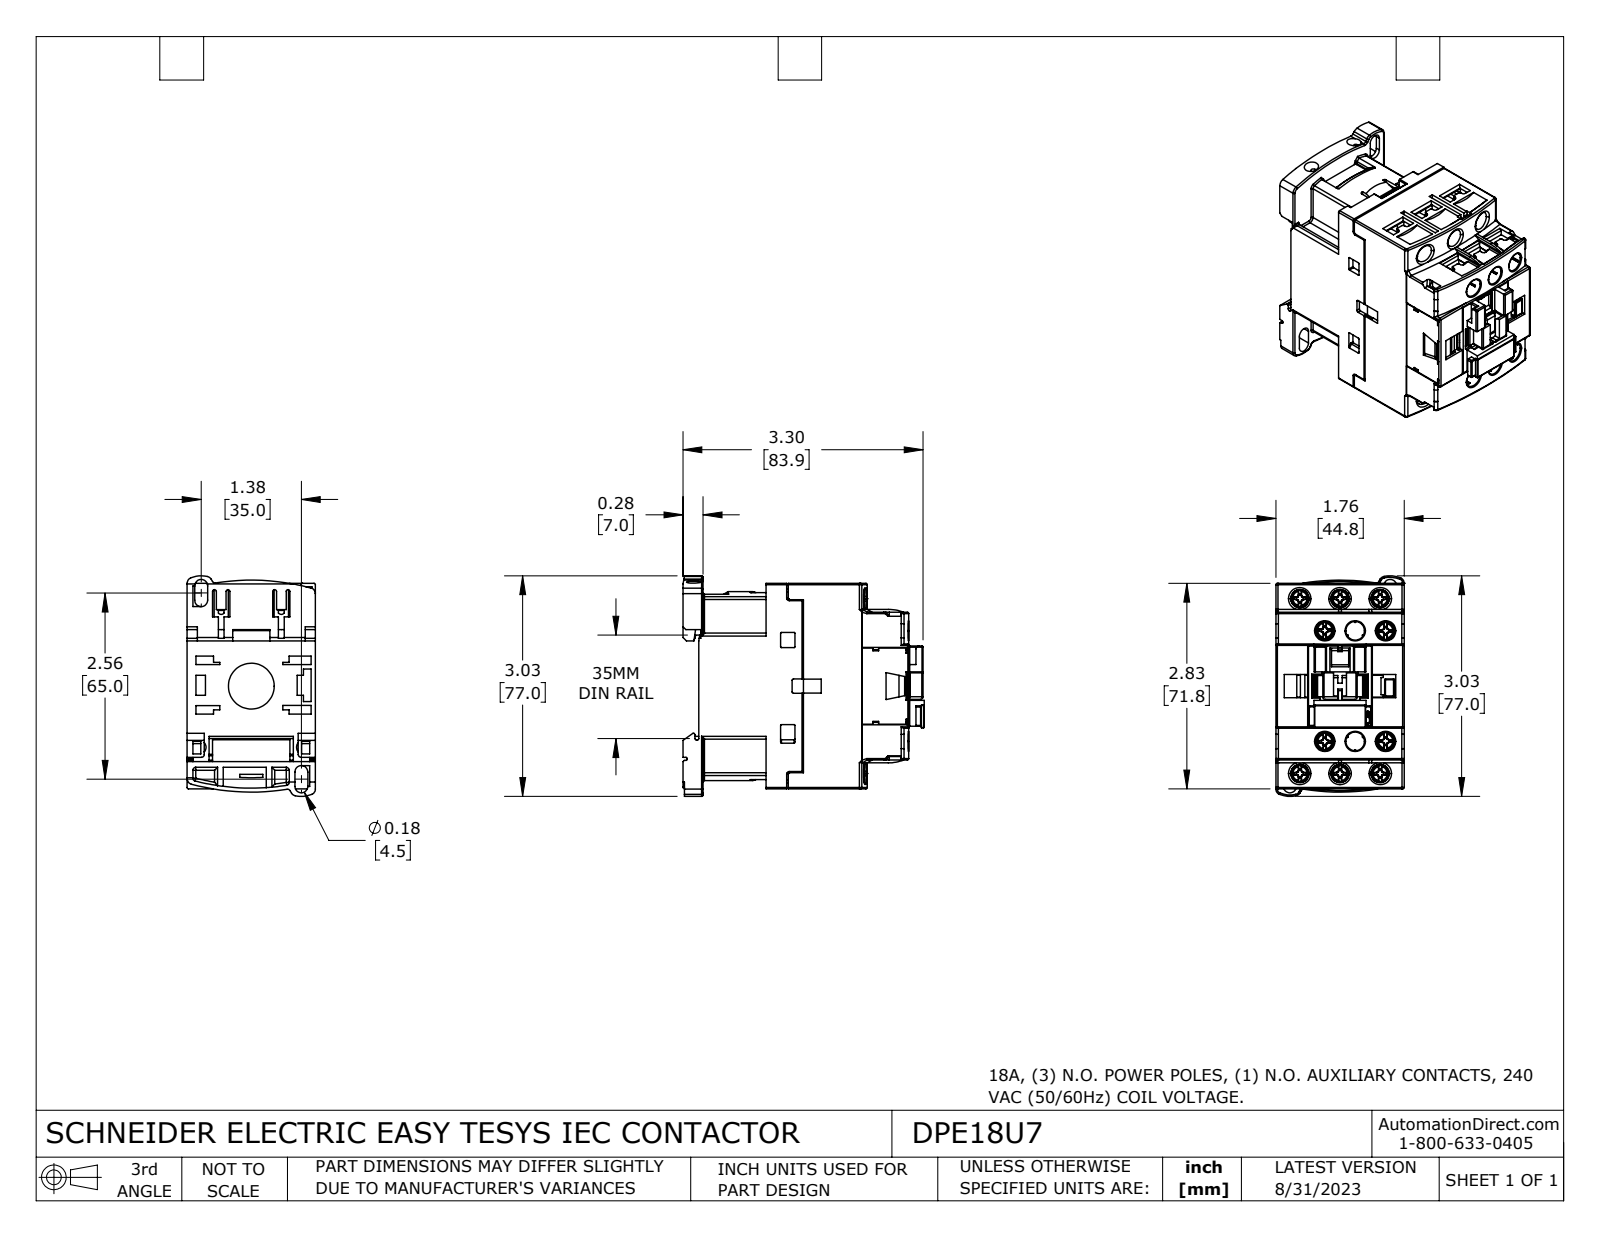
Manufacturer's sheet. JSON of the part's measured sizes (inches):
{"part_name": "DPE18U7", "step_written_by": "SolidWorks 2021 (CONFIG_CONTROL_DESIGN)", "units": "inches", "bodies": {"solids": 20, "faces": 3363, "planar": 2297, "cylindrical": 694, "other": 372}, "overall_size": [3.317, 3.031, 1.783], "volume_in3": 8.907, "surface_area_in2": 103.4, "round_holes": [[0.252, 6], [0.256, 6], [0.197, 2], [0.167, 1], [0.63, 1]], "round_bosses_or_shafts": [[0.138, 10], [0.108, 10], [0.315, 6]], "partial_cylinders_radius": [[0.02, 78], [0.012, 64], [0.039, 61], [0.006, 42], [0.016, 24], [0.63, 9], [0.024, 8], [0.079, 7]], "face_to_face_distances": [0.047, 1.764, 1.717, 0.321, 1.128, 0.807, 0.35, 2.78, 1.366, 1.118], "hole_center_spacings": [0.417, 0.488, 0.551, 0.558, 0.788, 0.878, 1.321, 1.576]}
